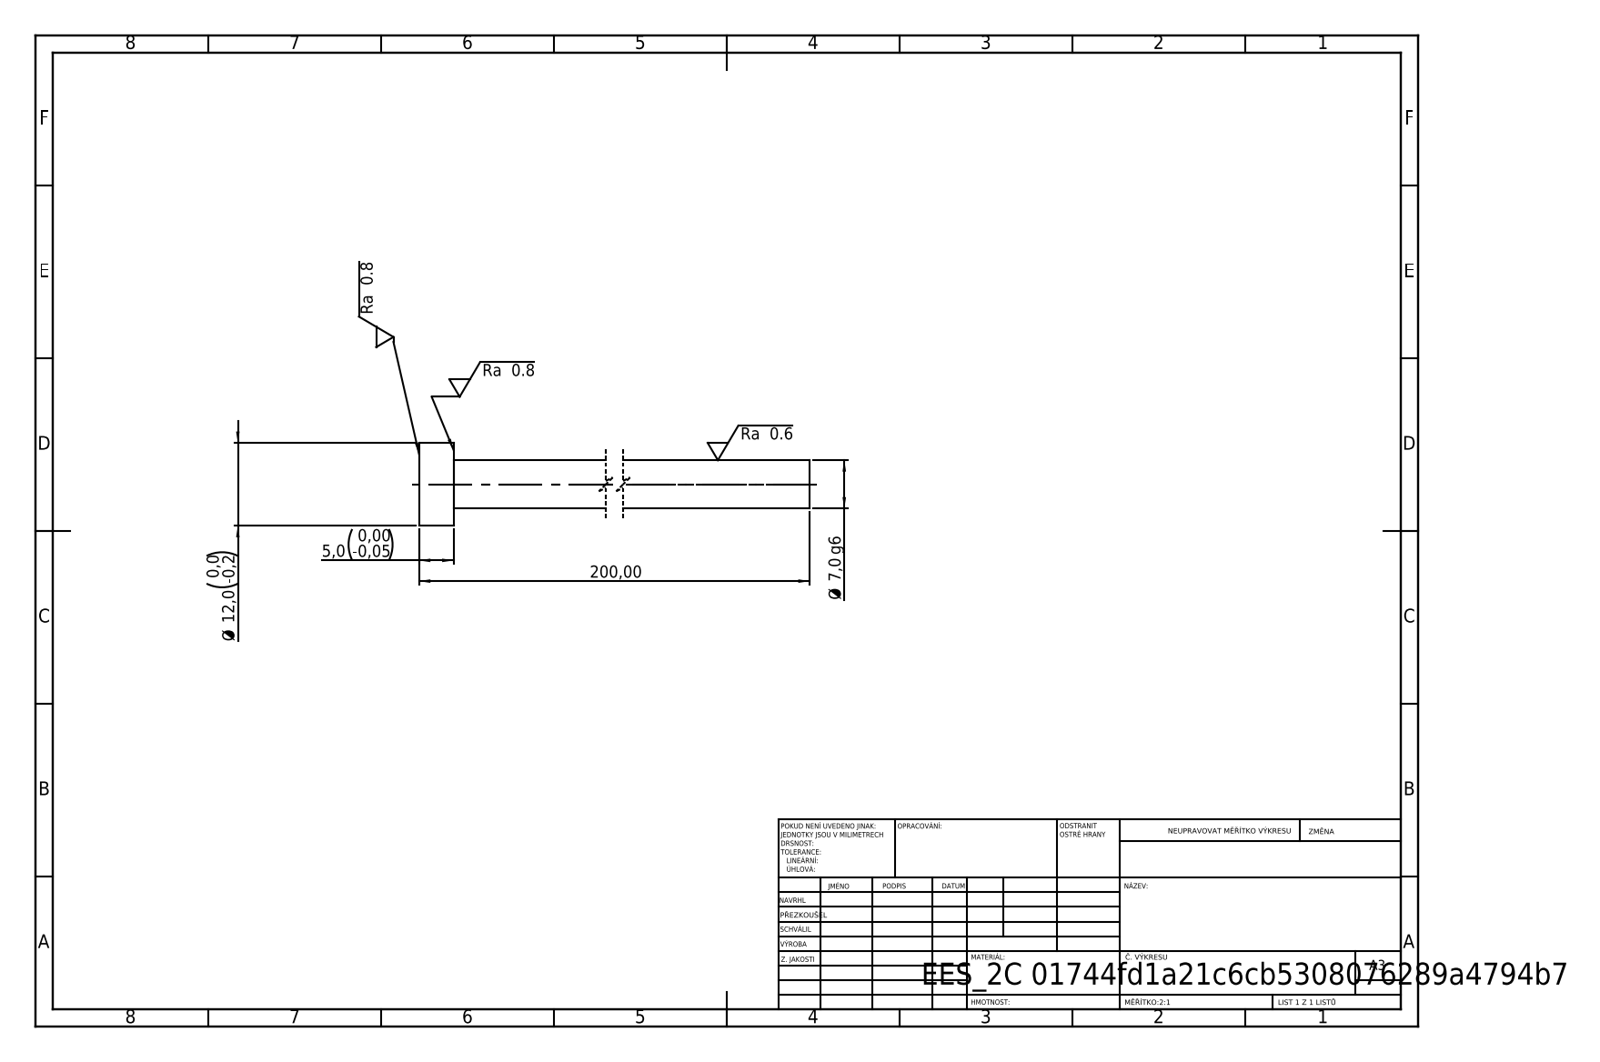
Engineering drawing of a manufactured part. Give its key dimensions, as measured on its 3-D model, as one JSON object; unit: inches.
{"step_written_by": "SolidWorks 2019 (CONFIG_CONTROL_DESIGN)", "units": "inches", "bodies": {"solids": 1, "faces": 7, "planar": 3, "cylindrical": 4, "other": 0}, "overall_size": [7.874, 0.472, 0.472], "volume_in3": 0.492, "surface_area_in2": 7.29, "round_bosses_or_shafts": [[0.472, 1], [0.276, 1]], "face_to_face_distances": [0.197, 7.874, 7.677]}
